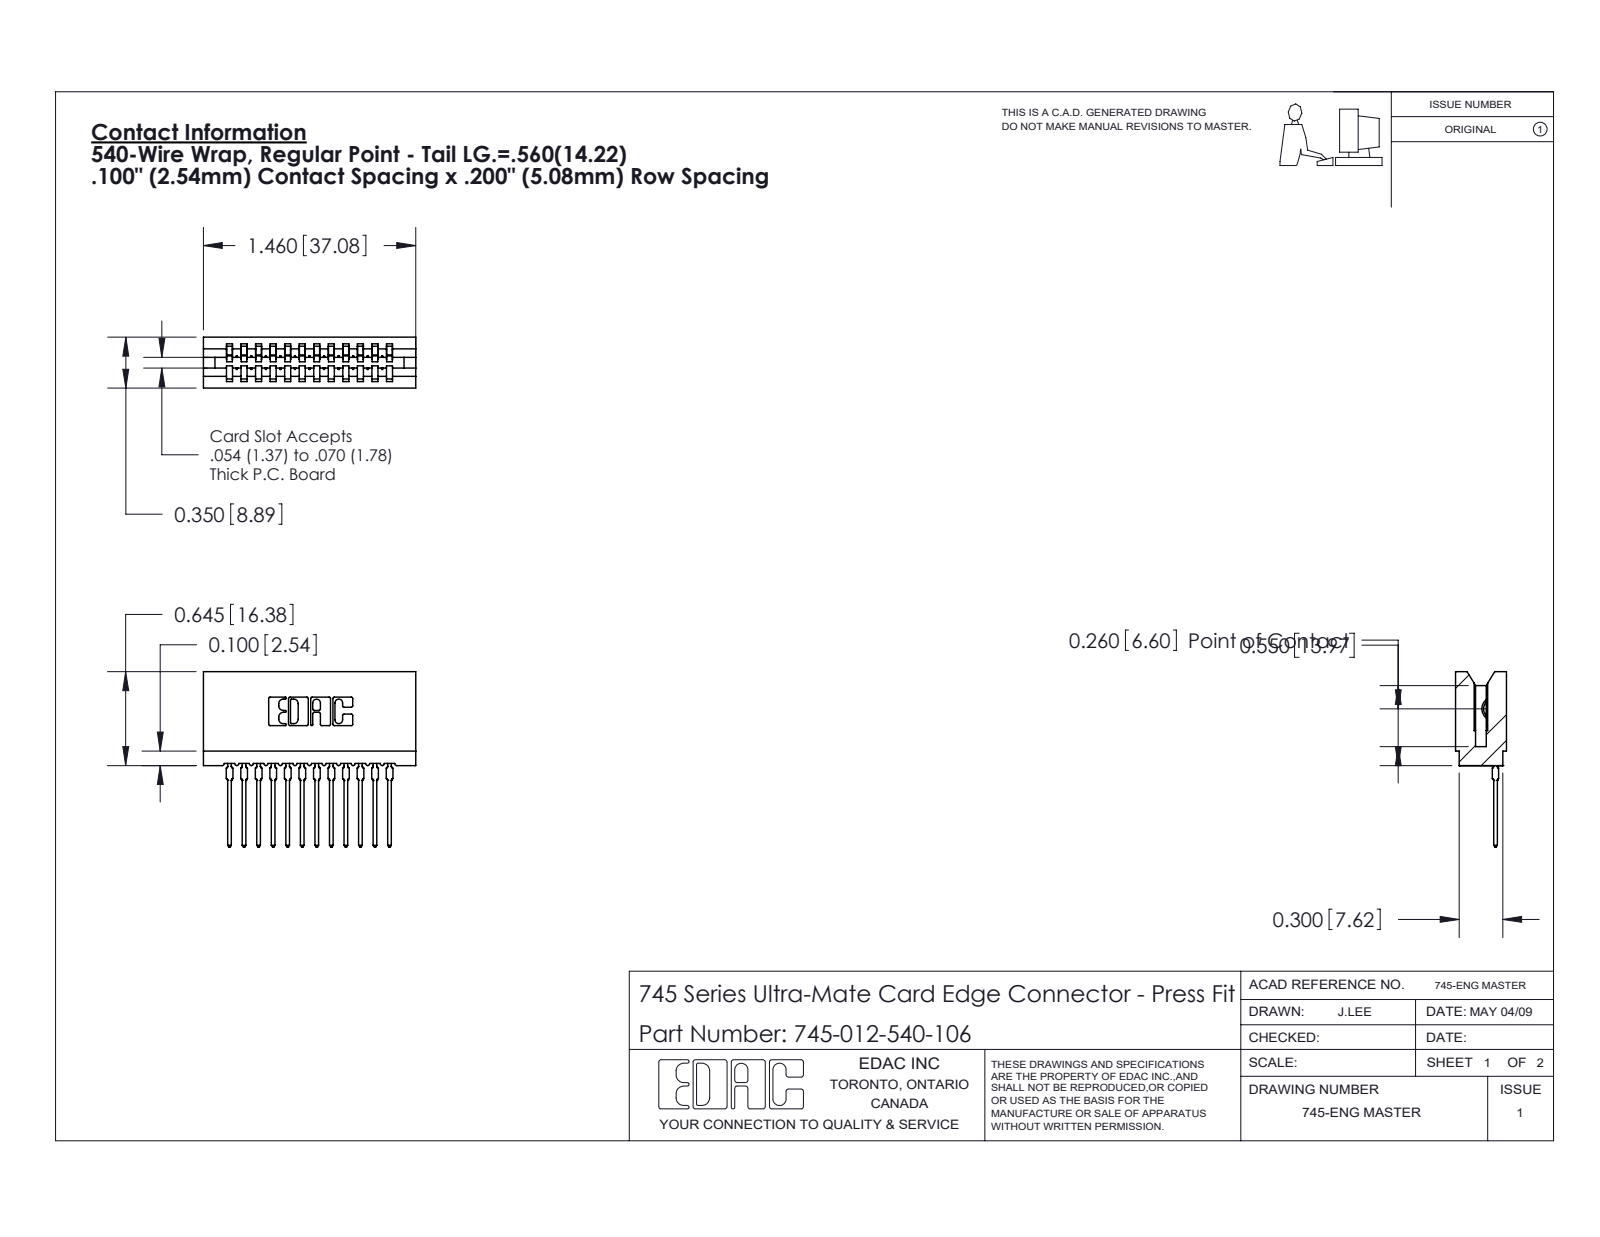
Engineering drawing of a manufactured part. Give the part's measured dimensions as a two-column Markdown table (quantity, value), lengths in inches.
| quantity | value |
| --- | --- |
| part name | 745-292-001_540; 745 Part_Insulator Option - 06; 745-012-540-106 |
| STEP written by | SolidWorks 2020 (CONFIG_CONTROL_DESIGN) |
| units | inches |
| bodies | 13 solids, 1440 faces (860 planar, 268 cylindrical, 312 other) |
| overall size | 1.46 × 1.206 × 0.35 |
| volume | 0.208 in³ |
| surface area | 9.19 in² |
| partial cylindrical surfaces (radius × count) | 0.015 × 24, 0.021 × 24, 0.01 × 22, 0.007 × 6, 0.031 × 6, 0.005 × 4, 0.011 × 4, 0.026 × 3 |
| main face-to-face distances | 0.1, 0.2, 0.3, 0.4, 0.5, 0.058, 0.6, 0.042, 0.35, 0.358 |
